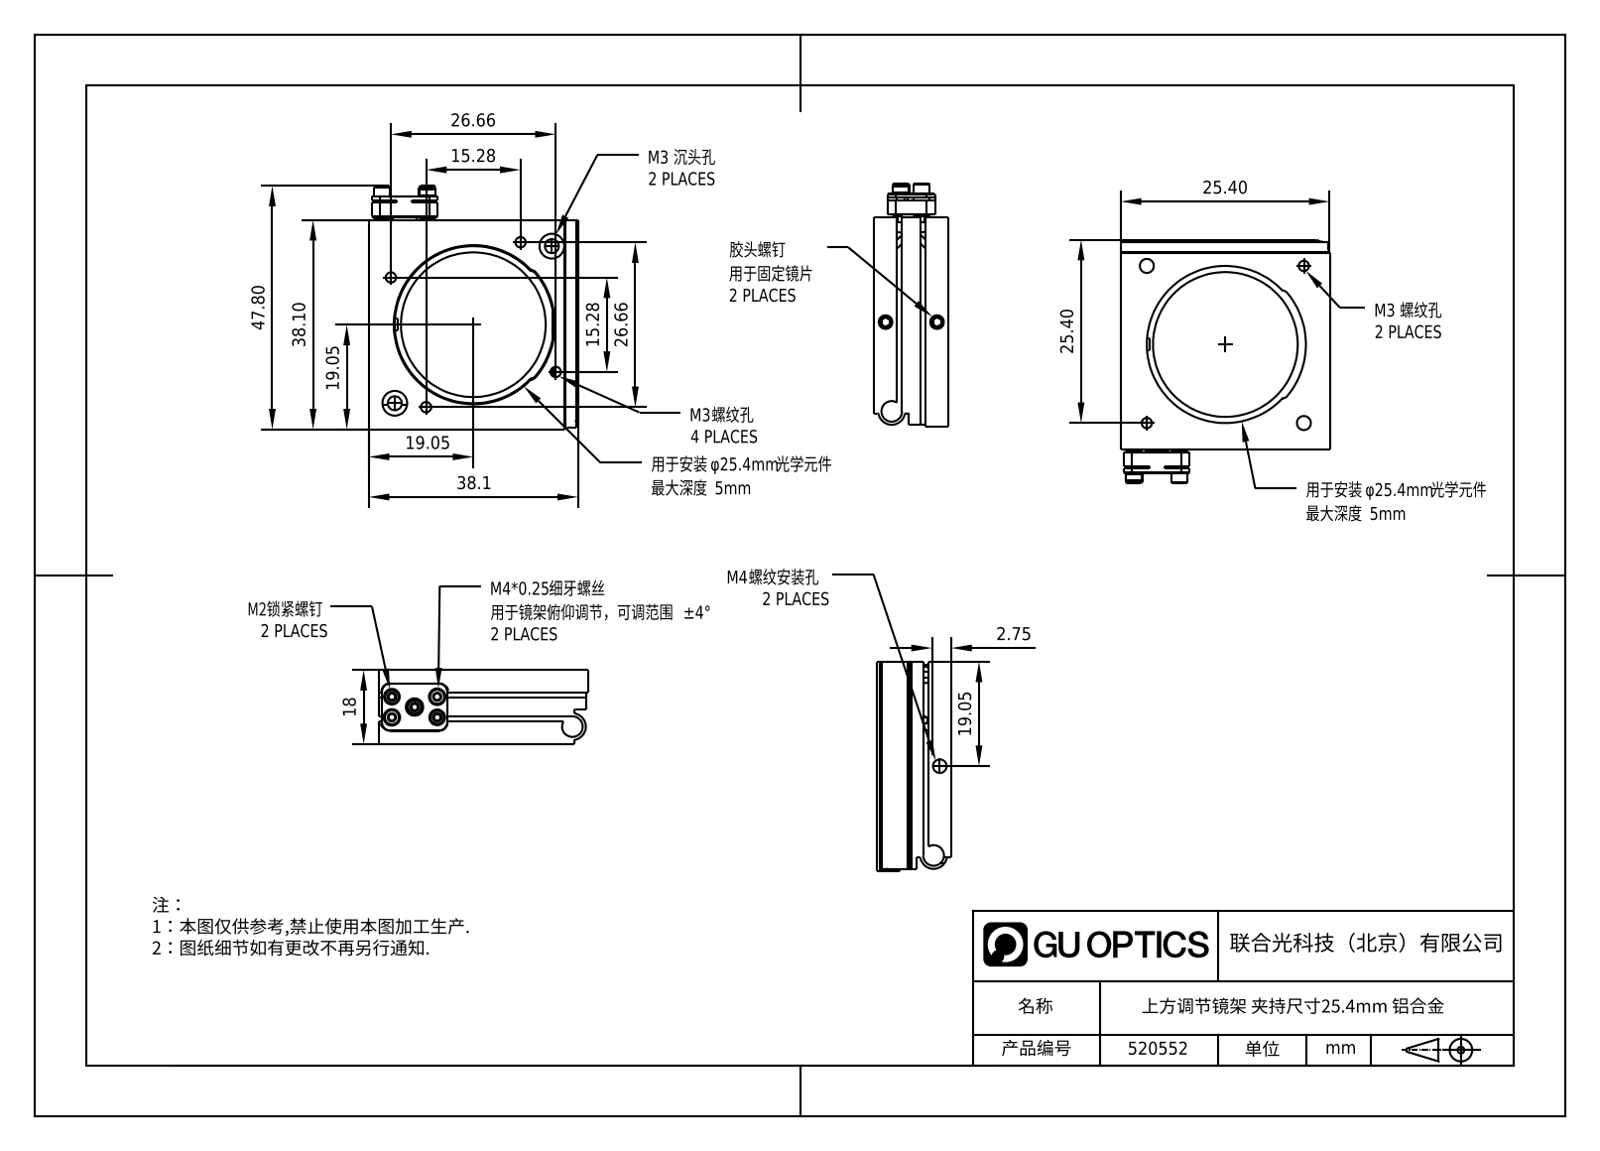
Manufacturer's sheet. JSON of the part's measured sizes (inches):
{"step_written_by": "SolidWorks 2021 (CONFIG_CONTROL_DESIGN)", "units": "inches", "bodies": {"solids": 0, "faces": 281, "planar": 97, "cylindrical": 118, "other": 66}, "overall_size": [1.849, 1.5, 0.709], "round_holes": [[0.098, 6], [0.13, 3], [0.059, 2], [0.134, 2], [0.197, 2], [0.236, 2], [0.157, 1], [0.882, 1], [1, 1]], "round_bosses_or_shafts": [[0.059, 4], [0.157, 2], [0.15, 2], [0.118, 1]], "partial_cylinders_radius": [[0.014, 6], [0.079, 5], [0.059, 4], [0.02, 2], [0.03, 2], [0.089, 2], [0.098, 2], [0.128, 2]], "face_to_face_distances": [0.226, 0.266, 0.443, 0.049, 0.217, 0.492, 0.177, 0.276, 0.709, 0.02], "hole_center_spacings": [0.201, 0.605, 0.707, 0.801, 0.856, 1, 1.044, 1.3]}
